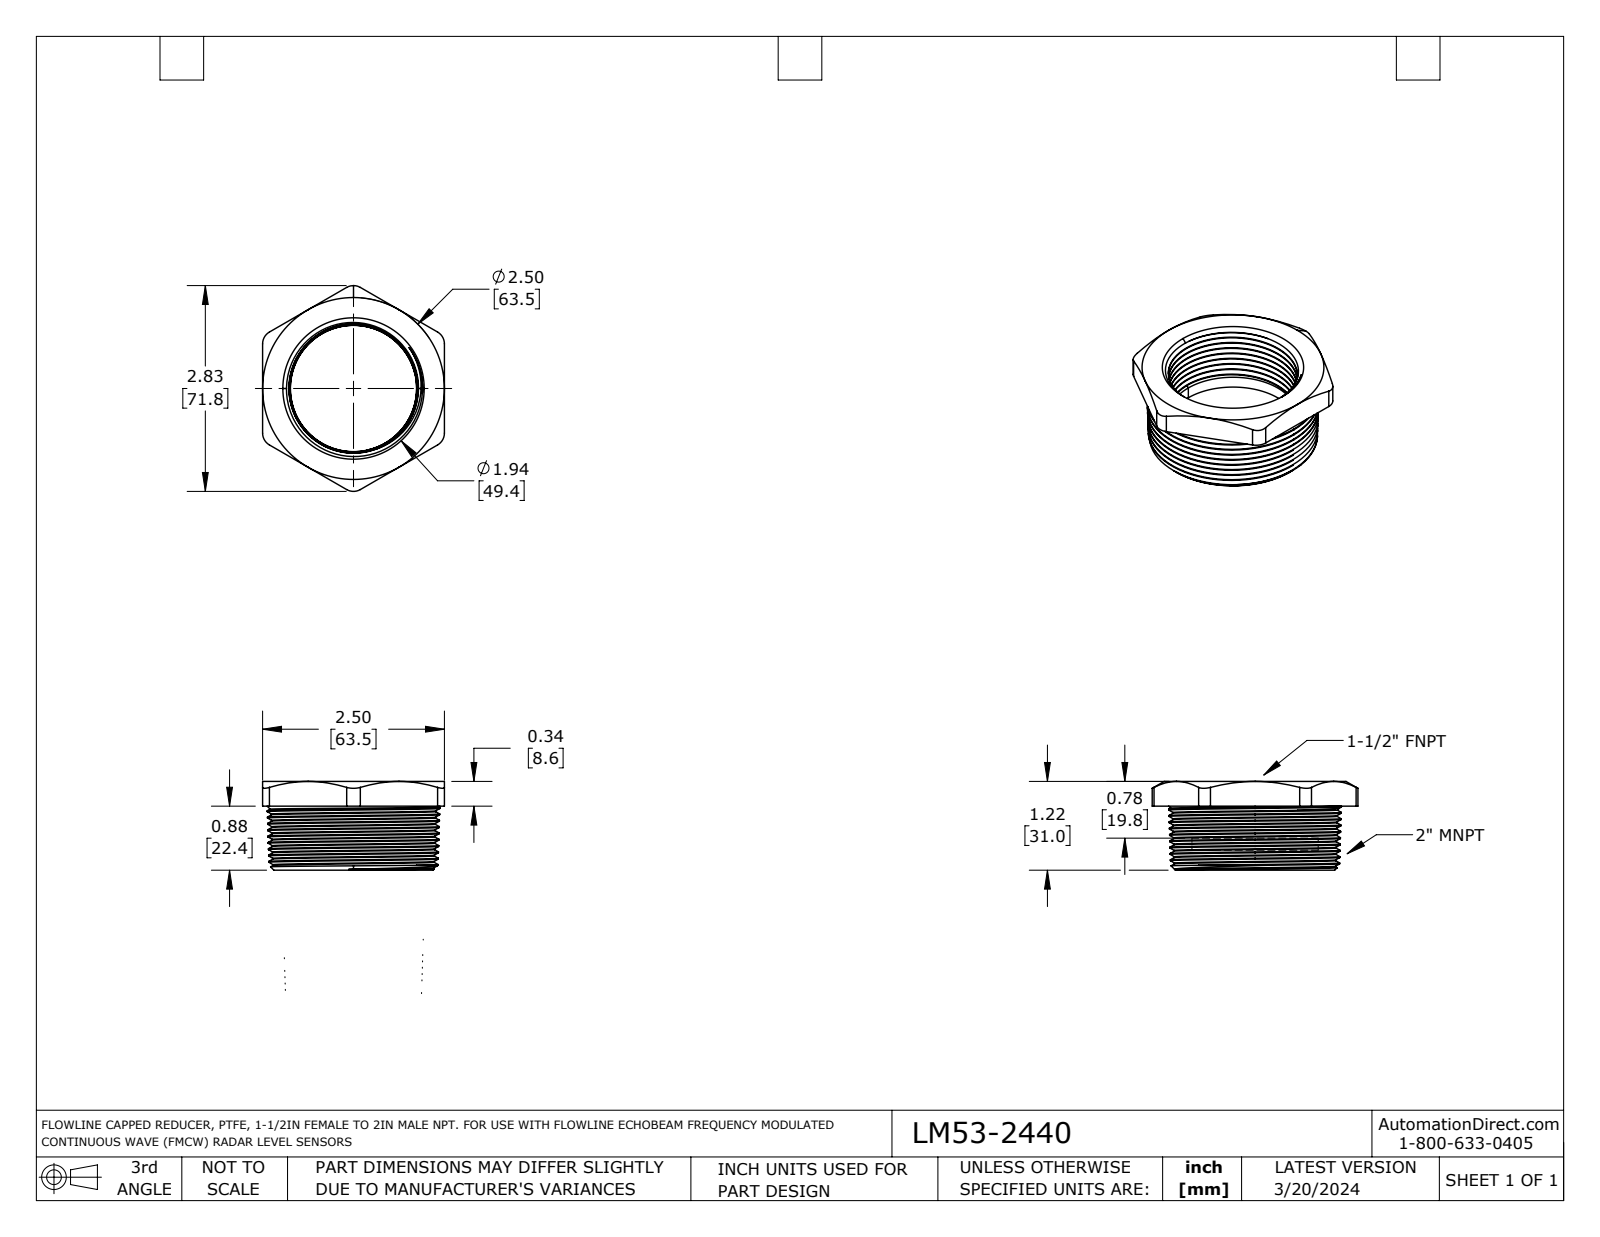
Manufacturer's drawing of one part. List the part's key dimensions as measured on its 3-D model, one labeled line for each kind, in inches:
Part name (STEP PRODUCT): LM53-2440
STEP written by: SolidWorks 2021 (AUTOMOTIVE_DESIGN)
Units: inches
Bodies: 1 solid, 93 faces (10 planar, 8 cylindrical, 75 other)
Overall size (bounding box): 2.829 × 2.5 × 1.22
Volume: 2.849 in³ · Surface area: 31.7 in²
Round holes (diameter × count): ⌀1.736 ×1
Partial cylindrical surfaces — rounded edges, fillets, slot ends (radius × count): R0.187 ×4, R0.188 ×2
Main face-to-face distances: 0.945, 2.5, 0.605, 0.34, 0.275, 0.88, 1.22
